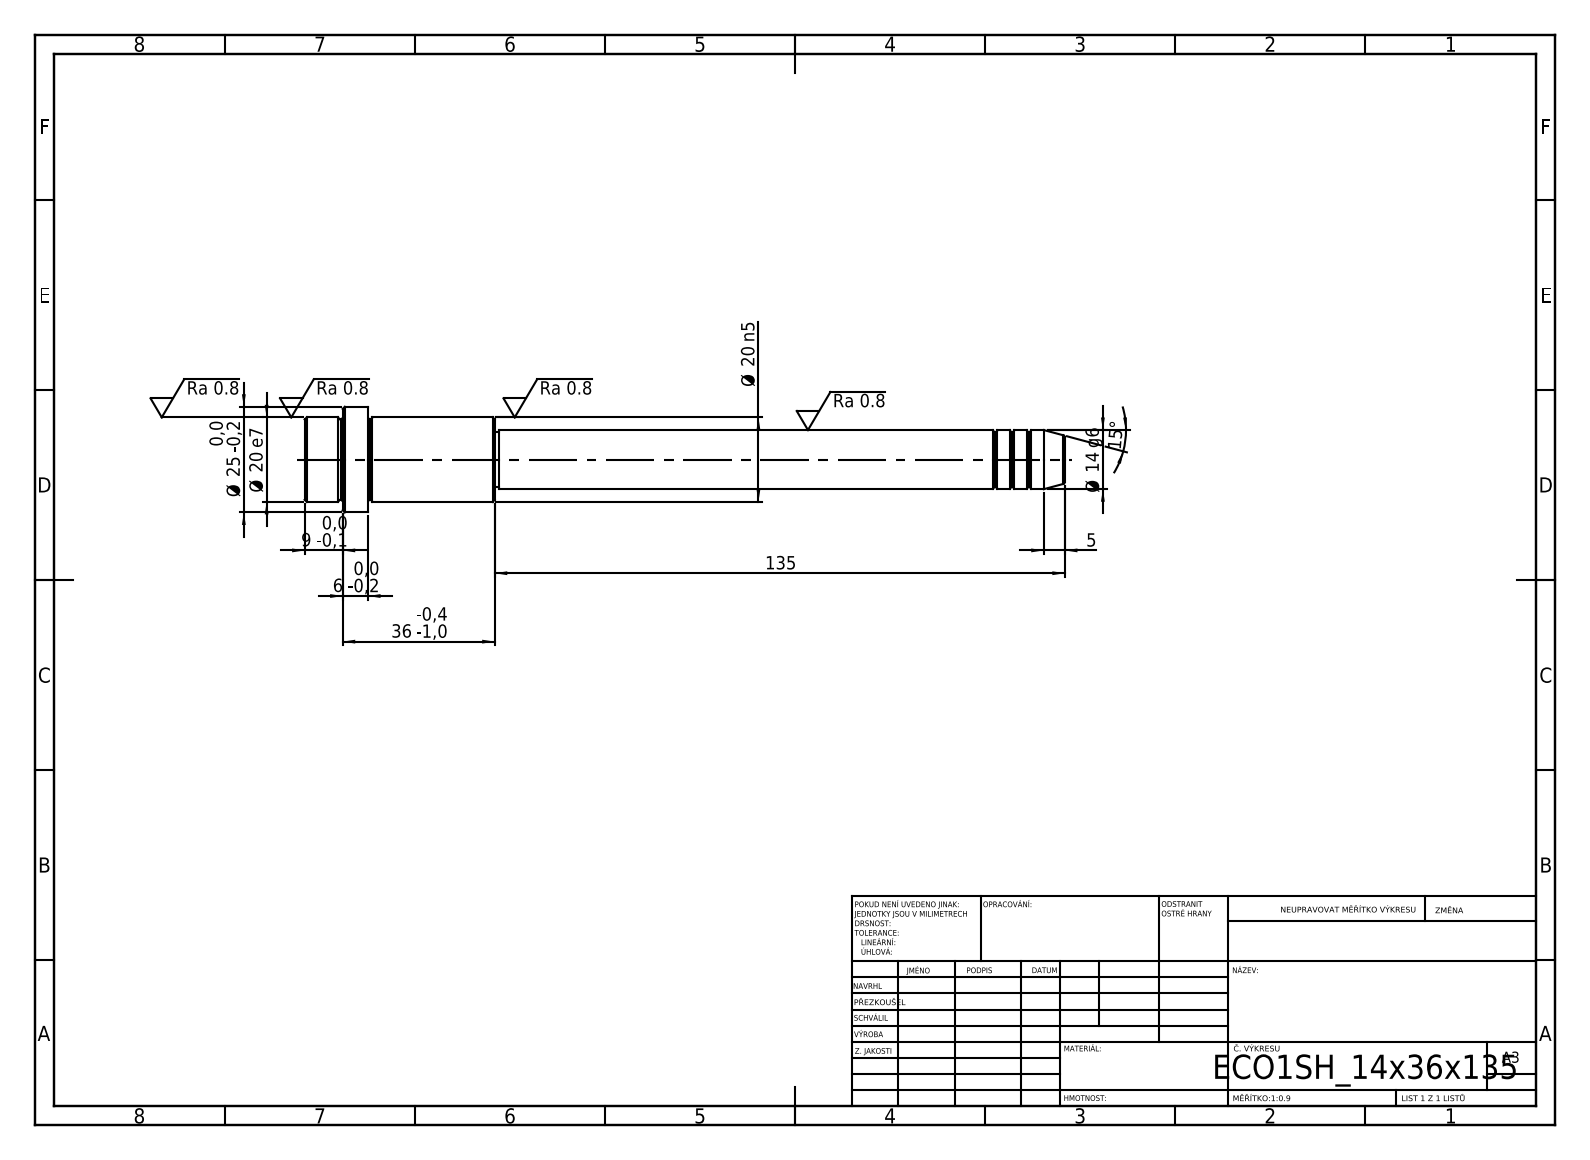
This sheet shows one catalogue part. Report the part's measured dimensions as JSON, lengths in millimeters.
{"step_written_by": "SolidWorks 2019 (CONFIG_CONTROL_DESIGN)", "units": "millimeters", "bodies": {"solids": 1, "faces": 52, "planar": 6, "cylindrical": 16, "other": 30}, "overall_size": [180, 25, 25], "volume_mm3": 35695, "surface_area_mm2": 9879, "round_bosses_or_shafts": [[25, 1], [20, 1], [14, 1], [13, 1]], "face_to_face_distances": [15, 30, 45, 36, 6, 9, 135, 165, 171, 180]}
